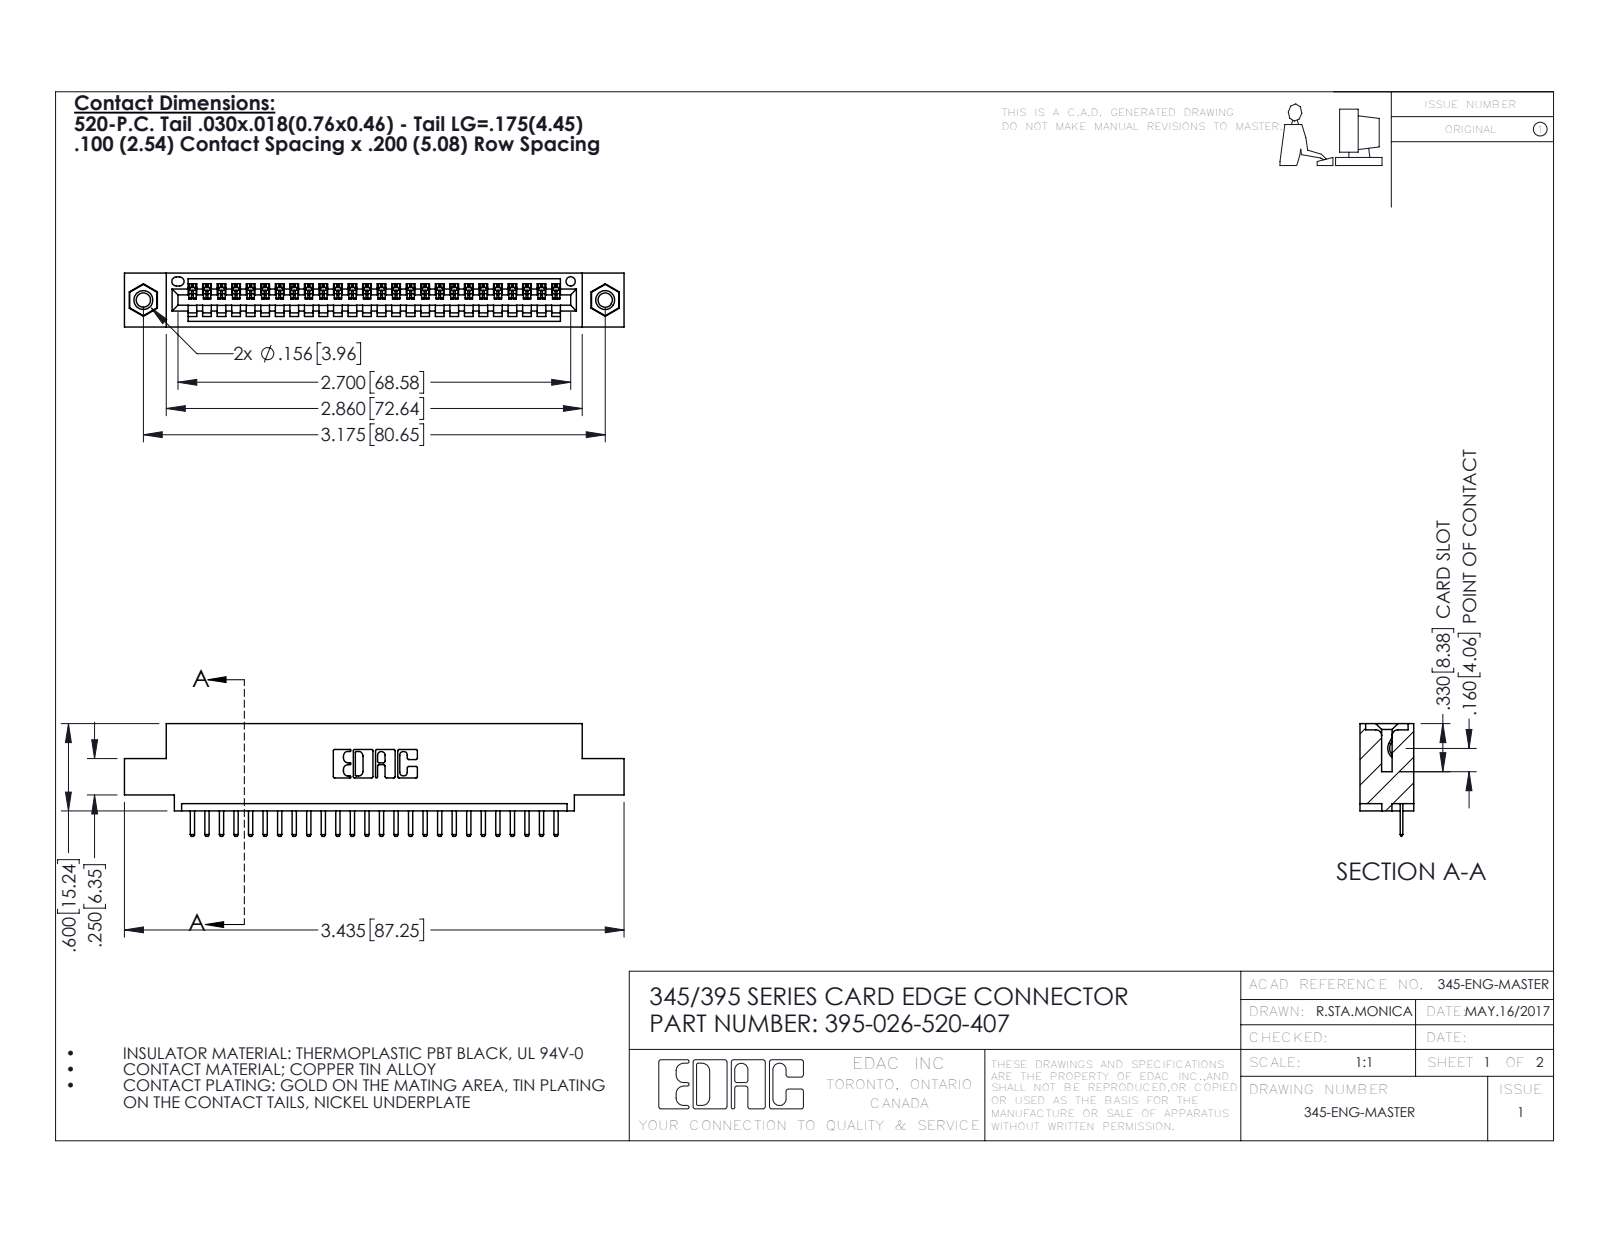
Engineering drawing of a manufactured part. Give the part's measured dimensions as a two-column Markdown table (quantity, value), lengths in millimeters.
| quantity | value |
| --- | --- |
| part name | 345 Part_0.110 Offset - 0.156 Dia-TI; 345-292-001_345-293-120; 395-026-520-407; 345-250-001_345-250-005-103 |
| STEP written by | SolidWorks 2016 (CONFIG_CONTROL_DESIGN) |
| units | millimeters |
| bodies | 29 solids, 1802 faces (1208 planar, 578 cylindrical, 16 other) |
| overall size | 87.2 × 19.7 × 9.4 |
| volume | 8 000 mm³ |
| surface area | 10 280 mm² |
| round holes (diameter × count) | 2.5 × 2, 3.2 × 2, 4 × 2, 1.6 × 1 |
| round bosses / shafts (diameter × count) | 3.9 × 2 |
| partial cylindrical surfaces (radius × count) | 0.3 × 54, 0.2 × 52, 0.3 × 22, 0.2 × 6, 0.8 × 6, 0.7 × 3, 0.8 × 2, 1 × 2 |
| main face-to-face distances | 1.8, 7.6, 9.4, 5.1, 2.5, 6.9, 0.6, 5.7, 1.8, 3.8 |
| hole center spacings | 6.9, 74.7, 80.6 |
